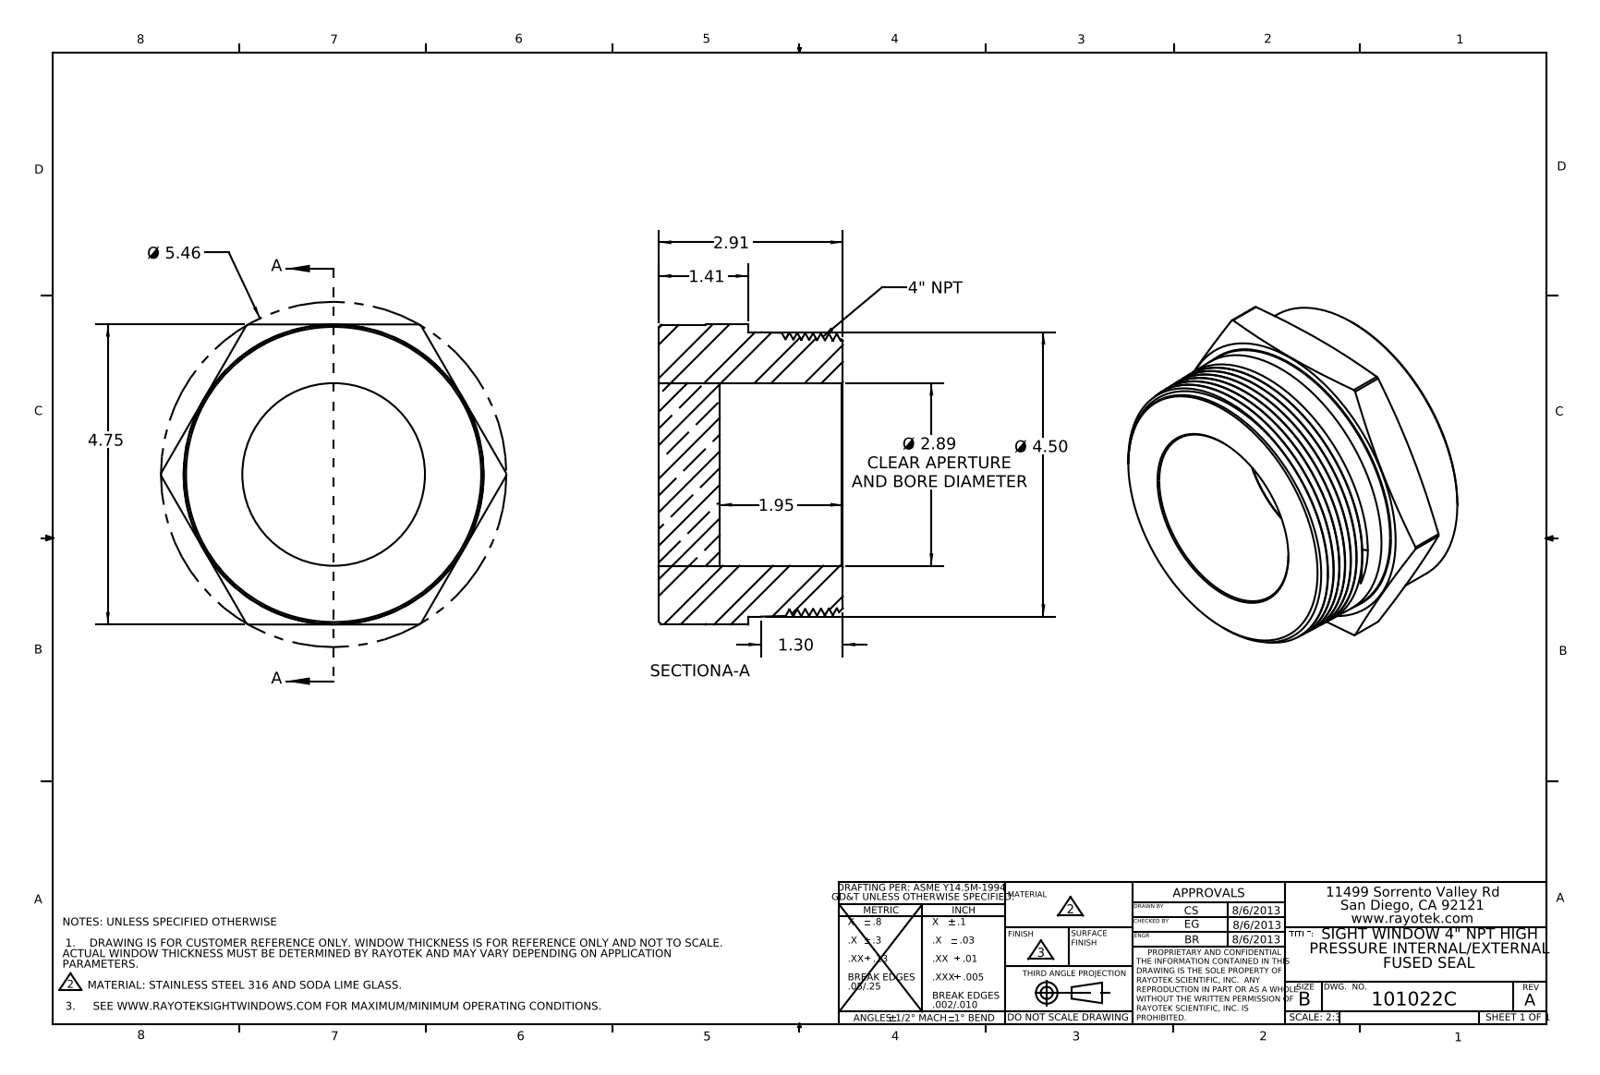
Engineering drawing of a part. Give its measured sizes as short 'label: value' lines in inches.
name: 101022; 402022; 403022_CUSTOMER
written by: SolidWorks 2012 (AUTOMOTIVE_DESIGN)
unit: in
bodies: 2 solids, 62 faces (14 planar, 15 cylindrical, 33 other)
size: 5.465 × 4.75 × 2.91
volume: 36.1 in³; area: 125.2 in²
holes: 1× ⌀2.89
bosses: 1× ⌀4.73, 1× ⌀4.5
rounds: 1× R2.732
face distances: 2.91, 0.96, 1.95, 4.75, 1.41, 0.45, 1.5
